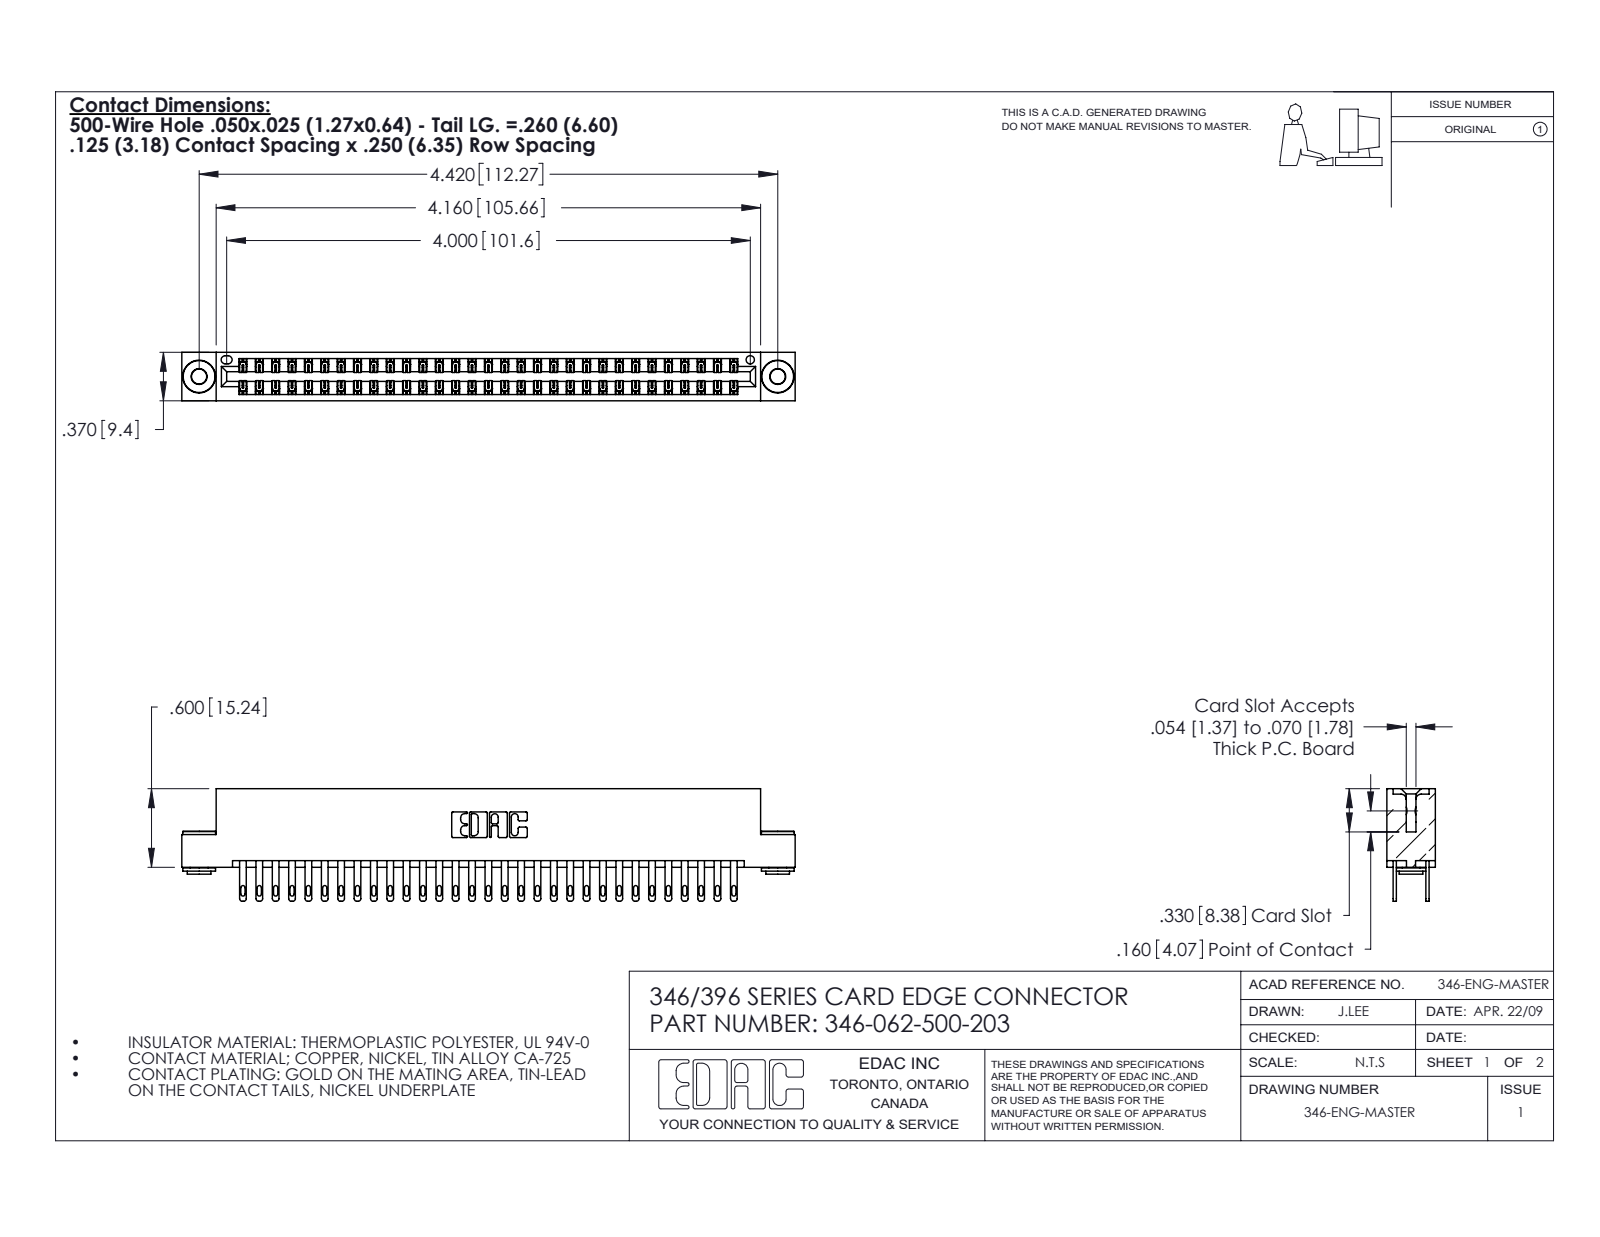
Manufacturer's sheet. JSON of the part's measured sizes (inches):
{"part_name": "346 Part_Flush Mounting Lugs - 0.156 Dia-TH; 345-292-001_345-293-100; 345-250-002_345-250-002-102; 346-062-500-203", "step_written_by": "SolidWorks 2020 (CONFIG_CONTROL_DESIGN)", "units": "inches", "bodies": {"solids": 65, "faces": 3150, "planar": 1898, "cylindrical": 1244, "other": 8}, "overall_size": [4.685, 0.86, 0.37], "volume_in3": 0.715, "surface_area_in2": 26.07, "round_holes": [[0.116, 2], [0.156, 2], [0.064, 1]], "round_bosses_or_shafts": [[0.25, 2], [0.18, 2], [0.136, 2]], "partial_cylinders_radius": [[0.006, 93], [0.016, 62], [0.02, 62], [0.01, 22], [0.007, 6], [0.031, 6], [0.026, 3], [0.014, 2]], "face_to_face_distances": [0.048, 0.322, 0.25, 0.025, 0.072, 0.298, 0.37, 0.275, 0.148, 0.222], "hole_center_spacings": [0.246, 4.212, 4.42]}
